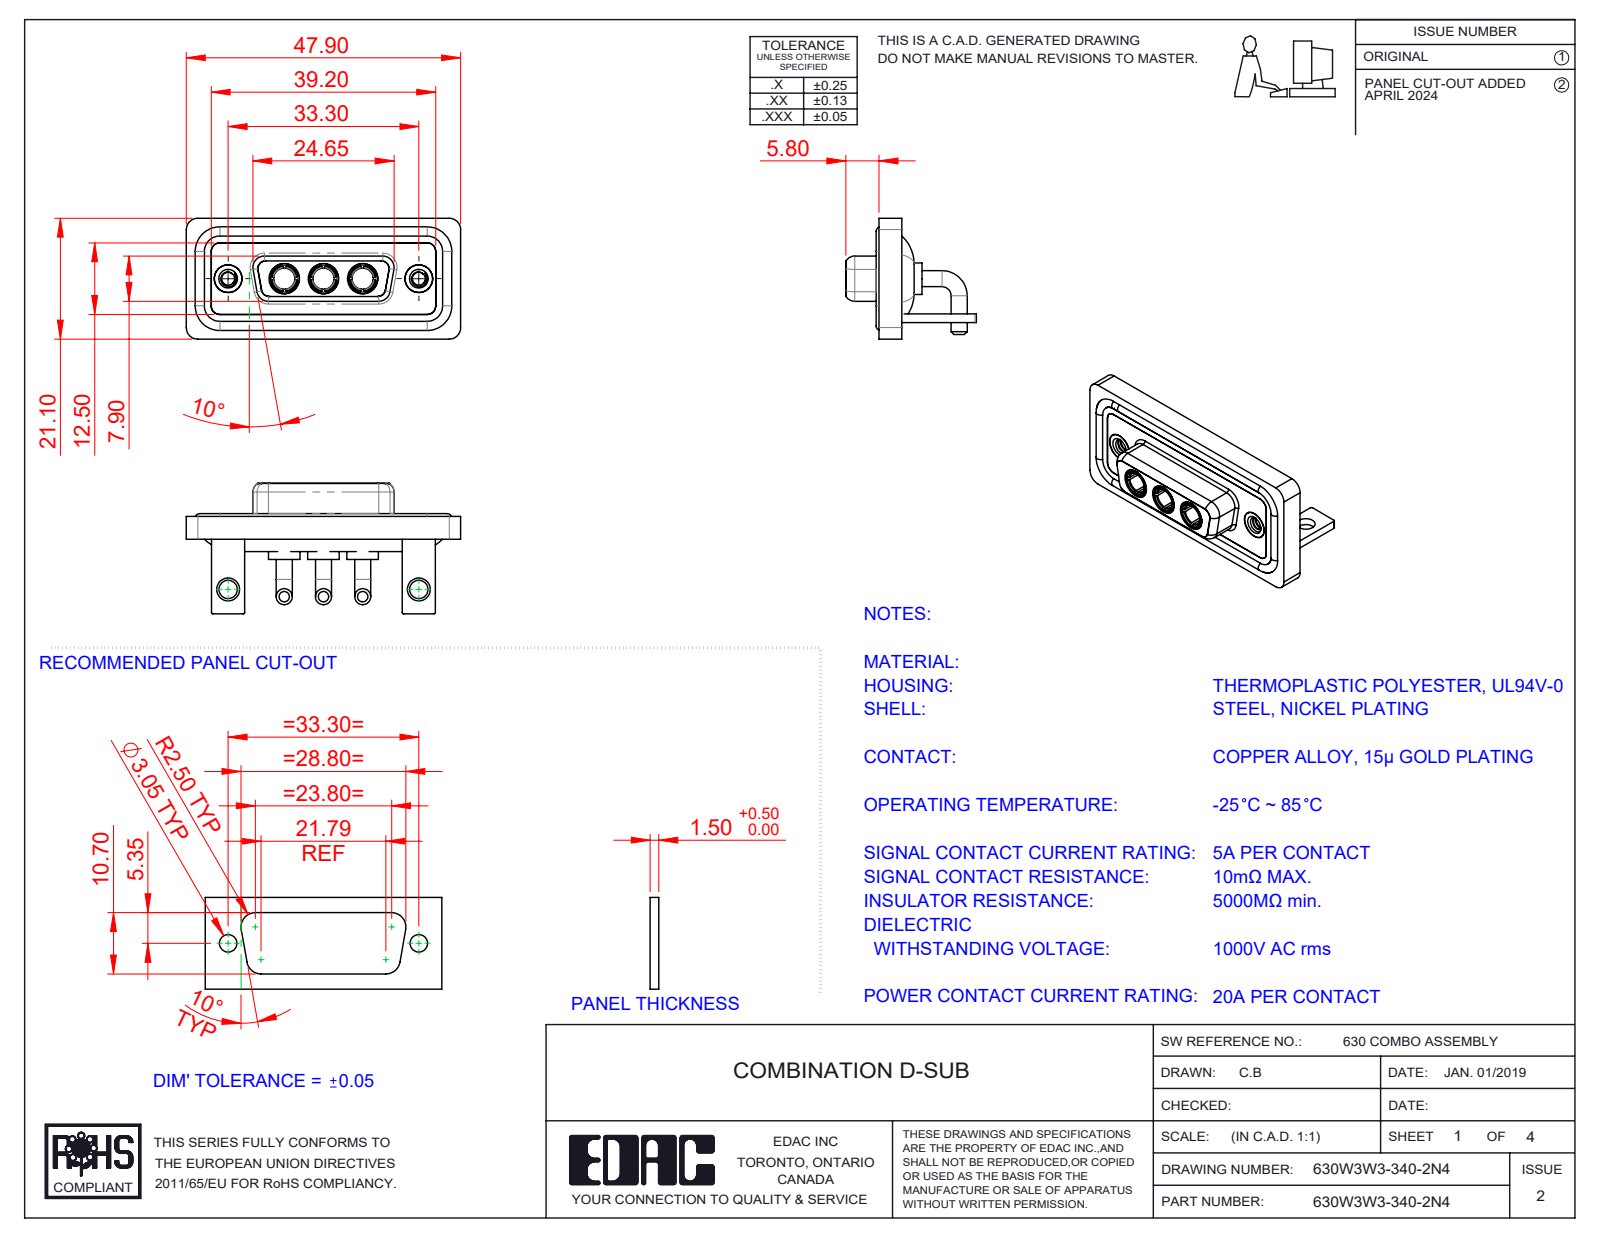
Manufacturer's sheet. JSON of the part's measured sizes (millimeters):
{"part_name": "630Combo Waterproof Housing_15 Contacts; 630W3W3-340-2N4; 630Combo Housing_3W3; 630Combo Shell Front_15 Contacts (+4 more)", "step_written_by": "SolidWorks 2023 (CONFIG_CONTROL_DESIGN)", "units": "millimeters", "bodies": {"solids": 15, "faces": 668, "planar": 212, "cylindrical": 287, "other": 169}, "overall_size": [47.9, 22.8, 21.1], "volume_mm3": 6546, "surface_area_mm2": 10707, "round_holes": [[4.85, 5], [3.7, 3], [5.3, 3], [2.26, 2], [3.2, 2], [4, 2], [4.05, 2], [5, 2]], "round_bosses_or_shafts": [[2.8, 6], [1.6, 4], [5.5, 3], [5.2, 3], [4.96, 3], [4.75, 3], [3.75, 3], [4.95, 2]], "partial_cylinders_radius": [[2, 21], [1.5, 18], [0.25, 16], [1.35, 12], [1.6, 8], [0.5, 5], [0.6, 4], [0.65, 4]], "face_to_face_distances": [0.4, 2.9, 1.5, 1.8, 3.7, 1.1, 4.1, 1.6, 2.5, 1.4], "hole_center_spacings": [6.85, 9.8, 16.65, 23.5, 33.3, 13.7]}
